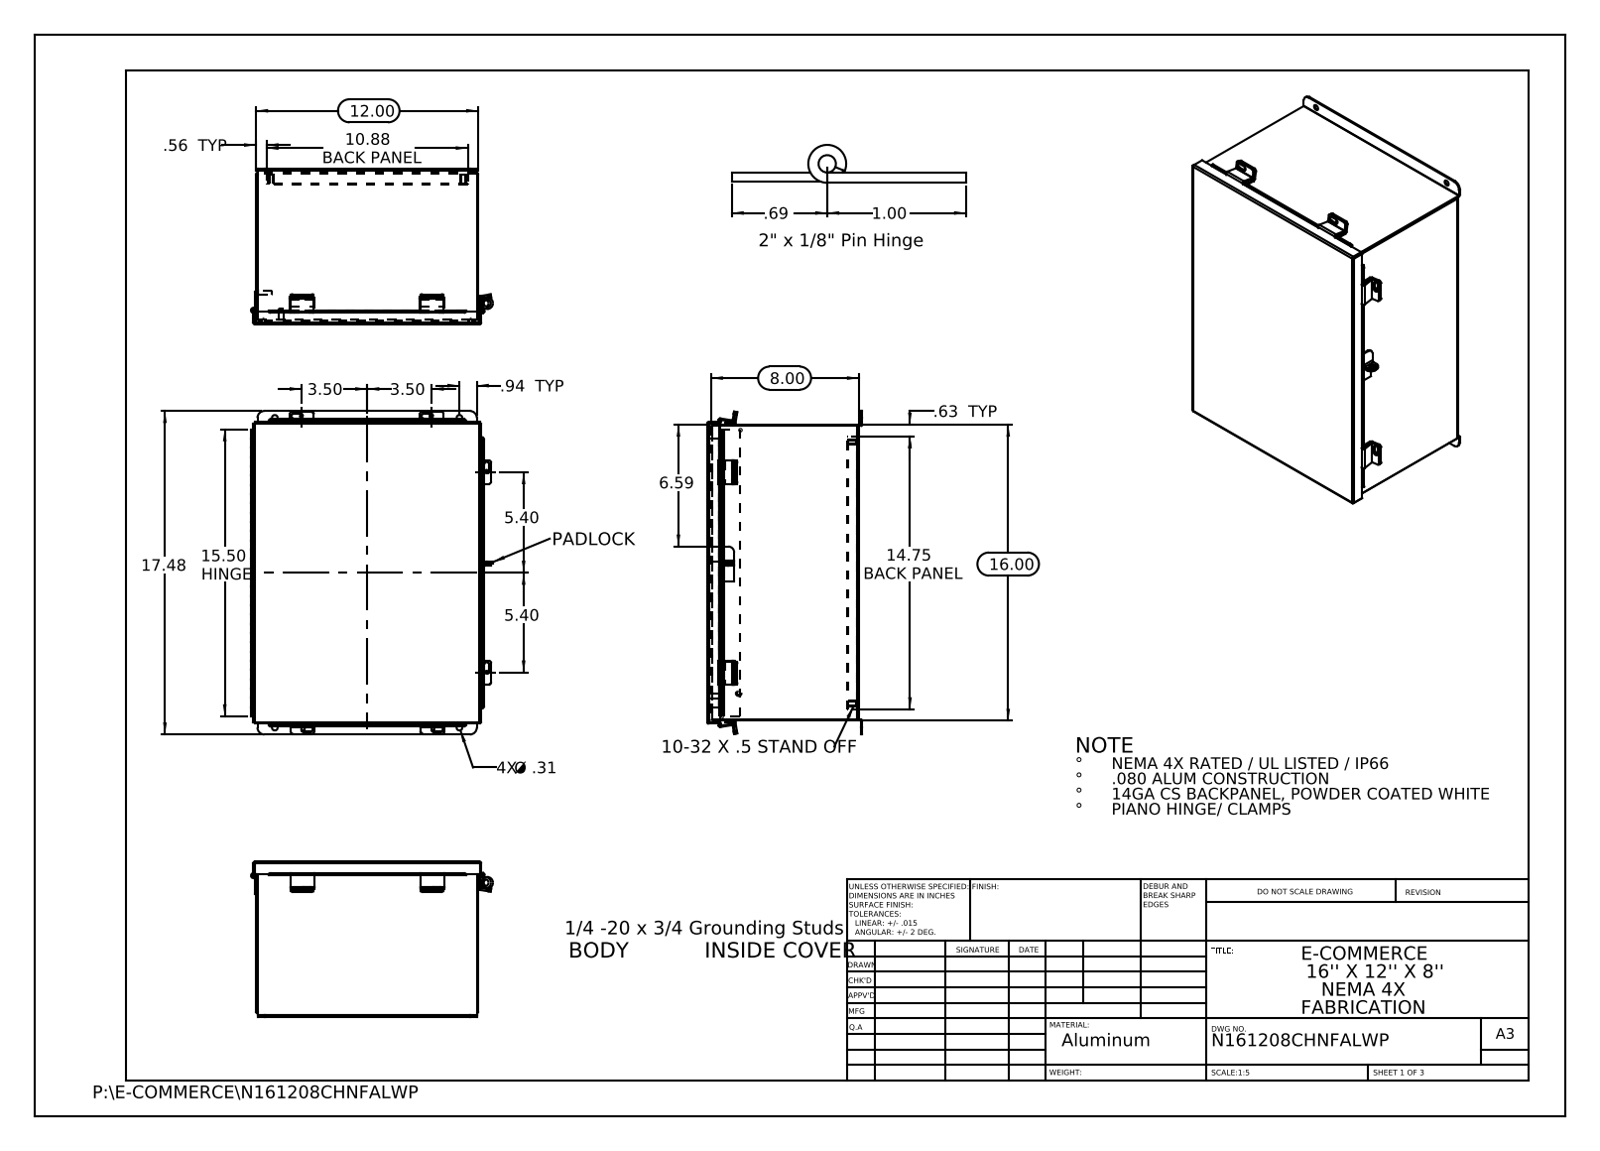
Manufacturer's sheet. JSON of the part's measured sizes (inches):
{"part_name": "HW-CLH-JH-20154; N161208CHNFALWP Hinge Cover Side JIC; N161208CHNFALWP JIC Backpanel; N161208CHNFALWP JIC Enclosure Template (+8 more)", "step_written_by": "SolidWorks 2013 (CONFIG_CONTROL_DESIGN)", "units": "inches", "bodies": {"solids": 27, "faces": 866, "planar": 539, "cylindrical": 307, "other": 20}, "overall_size": [17.476, 13.072, 8.39], "volume_in3": 83.73, "surface_area_in2": 2277, "round_holes": [[0.25, 10], [0.187, 4], [0.312, 4], [0.125, 1], [0.125, 1], [0.373, 1], [0.375, 1]], "round_bosses_or_shafts": [[0.313, 4], [0.315, 2], [0.236, 2], [0.273, 1], [0.25, 1]], "partial_cylinders_radius": [[0.125, 24], [0.013, 13], [0.009, 12], [0.088, 12], [0.133, 12], [0.083, 6], [0.1, 6], [0.375, 4]], "face_to_face_distances": [0.075, 8.128, 11.925, 15.925, 8.053, 8.203, 7.628, 0.575, 0.5, 7.553], "hole_center_spacings": [1.315, 10.258, 15.427, 18.48, 7, 9.976, 10.375, 14.126]}
